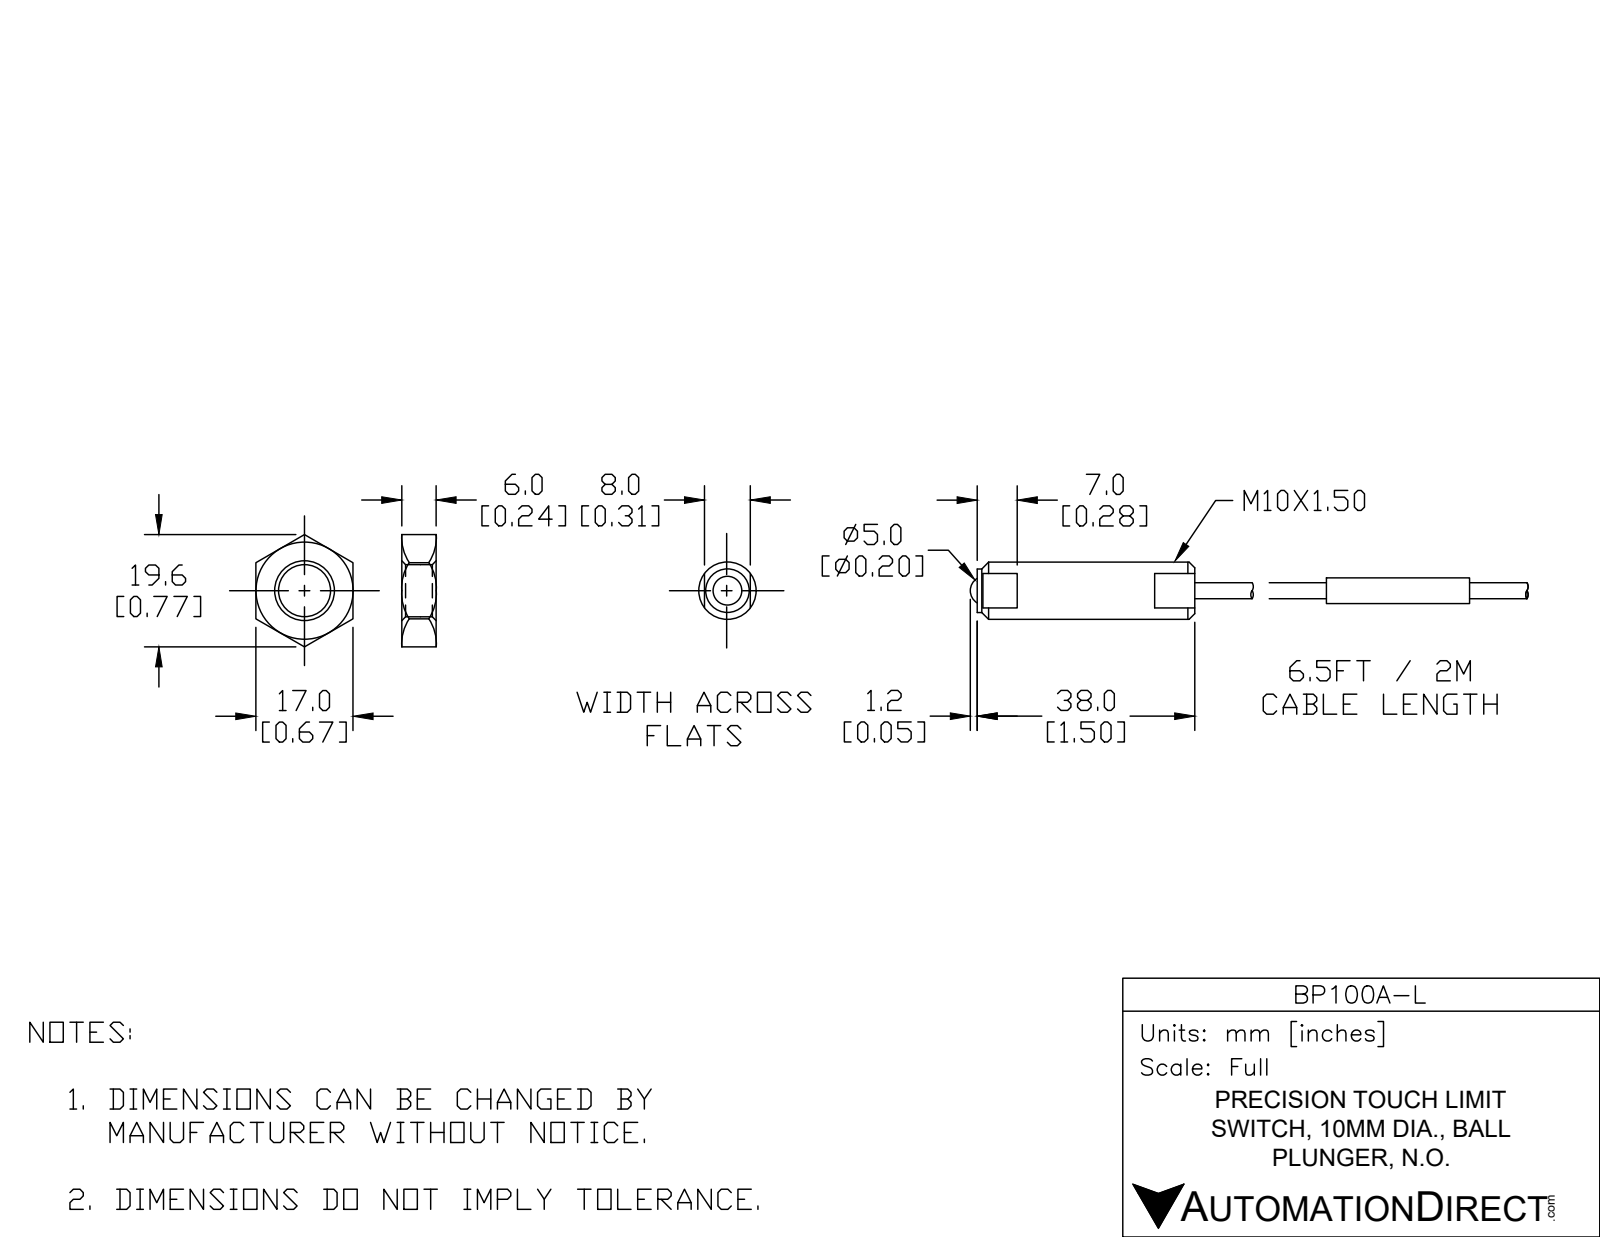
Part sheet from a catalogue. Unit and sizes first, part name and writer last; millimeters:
Units: millimetres
Overall size (bounding box): 97.2 × 10 × 10
Round bosses / shafts (diameter × count): ⌀10 ×1, ⌀7.6 ×1, ⌀4.5 ×1, ⌀2.8 ×1
Main face-to-face distances: 38, 8.58, 10.5, 12.5, 61, 86, 23, 48, 25, 48.5
Volume: 3 024 mm³ · Surface area: 2 421 mm²
Bodies: 2 solids, 129 faces (31 planar, 58 cylindrical, 40 other)
Part name (STEP PRODUCT): BP100A-L
STEP written by: SolidWorks 2017 (CONFIG_CONTROL_DESIGN)
